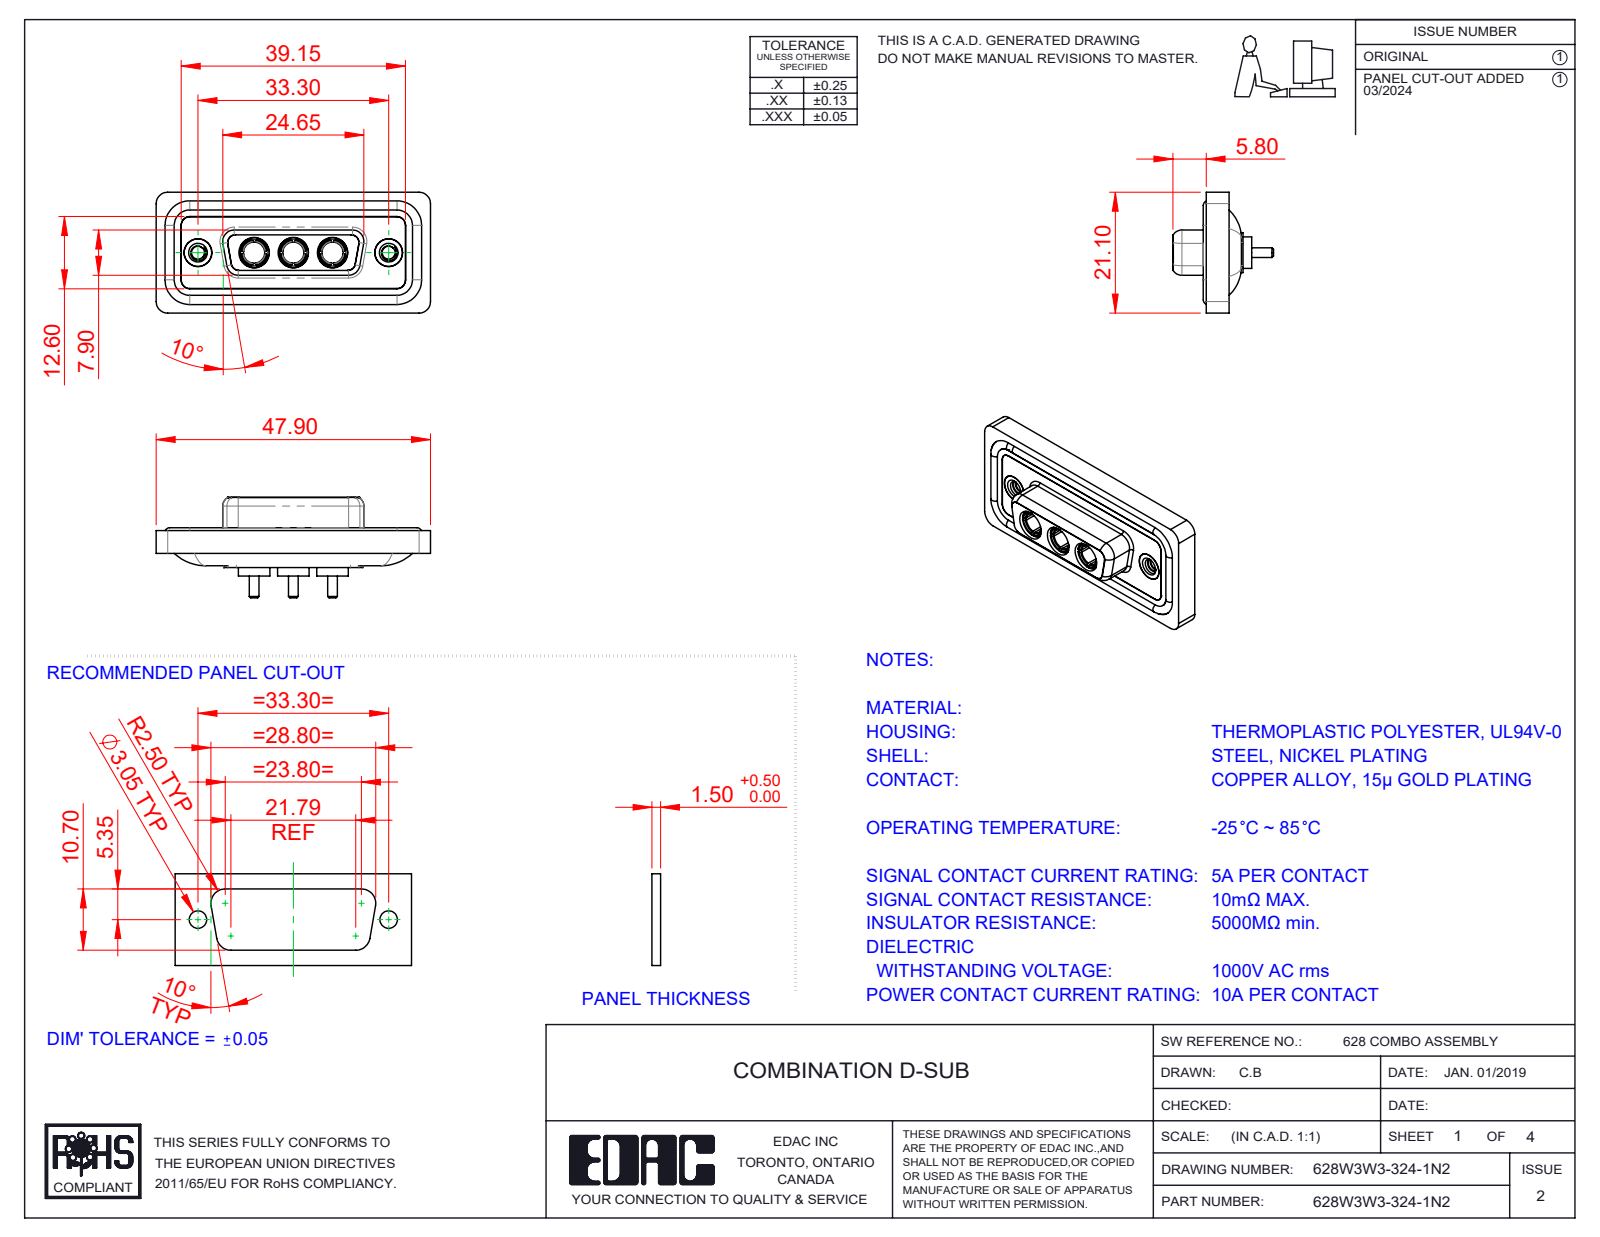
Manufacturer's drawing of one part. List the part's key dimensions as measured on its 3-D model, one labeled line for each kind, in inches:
Part name (STEP PRODUCT): 628Combo Housing_3W3; 628Combo Shell Rear_15 Contacts; 628Combo Waterproof Housing_15 Contacts; 628W3W3-324-1N2 (+3 more)
STEP written by: SolidWorks 2023 (CONFIG_CONTROL_DESIGN)
Units: inches
Bodies: 13 solids, 608 faces (192 planar, 257 cylindrical, 159 other)
Overall size (bounding box): 1.886 × 0.831 × 0.691
Volume: 0.365 in³ · Surface area: 15.04 in²
Round holes (diameter × count): ⌀0.191 ×5, ⌀0.146 ×3, ⌀0.209 ×3, ⌀0.089 ×2, ⌀0.157 ×2, ⌀0.159 ×2, ⌀0.197 ×2
Round bosses / shafts (diameter × count): ⌀0.063 ×4, ⌀0.217 ×3, ⌀0.205 ×3, ⌀0.195 ×3, ⌀0.187 ×3, ⌀0.148 ×3, ⌀0.067 ×3, ⌀0.195 ×2
Partial cylindrical surfaces — rounded edges, fillets, slot ends (radius × count): R0.059 ×22, R0.079 ×20, R0.053 ×12, R0.063 ×8, R0.01 ×4, R0.02 ×4, R0.024 ×4, R0.026 ×4
Main face-to-face distances: 0.016, 0.071, 0.063, 0.02, 0.293, 0.043, 0.114, 0.222, 0.278, 0.059
Hole centre spacings: 0.27, 0.386, 0.656, 0.925, 0.539, 1.311
